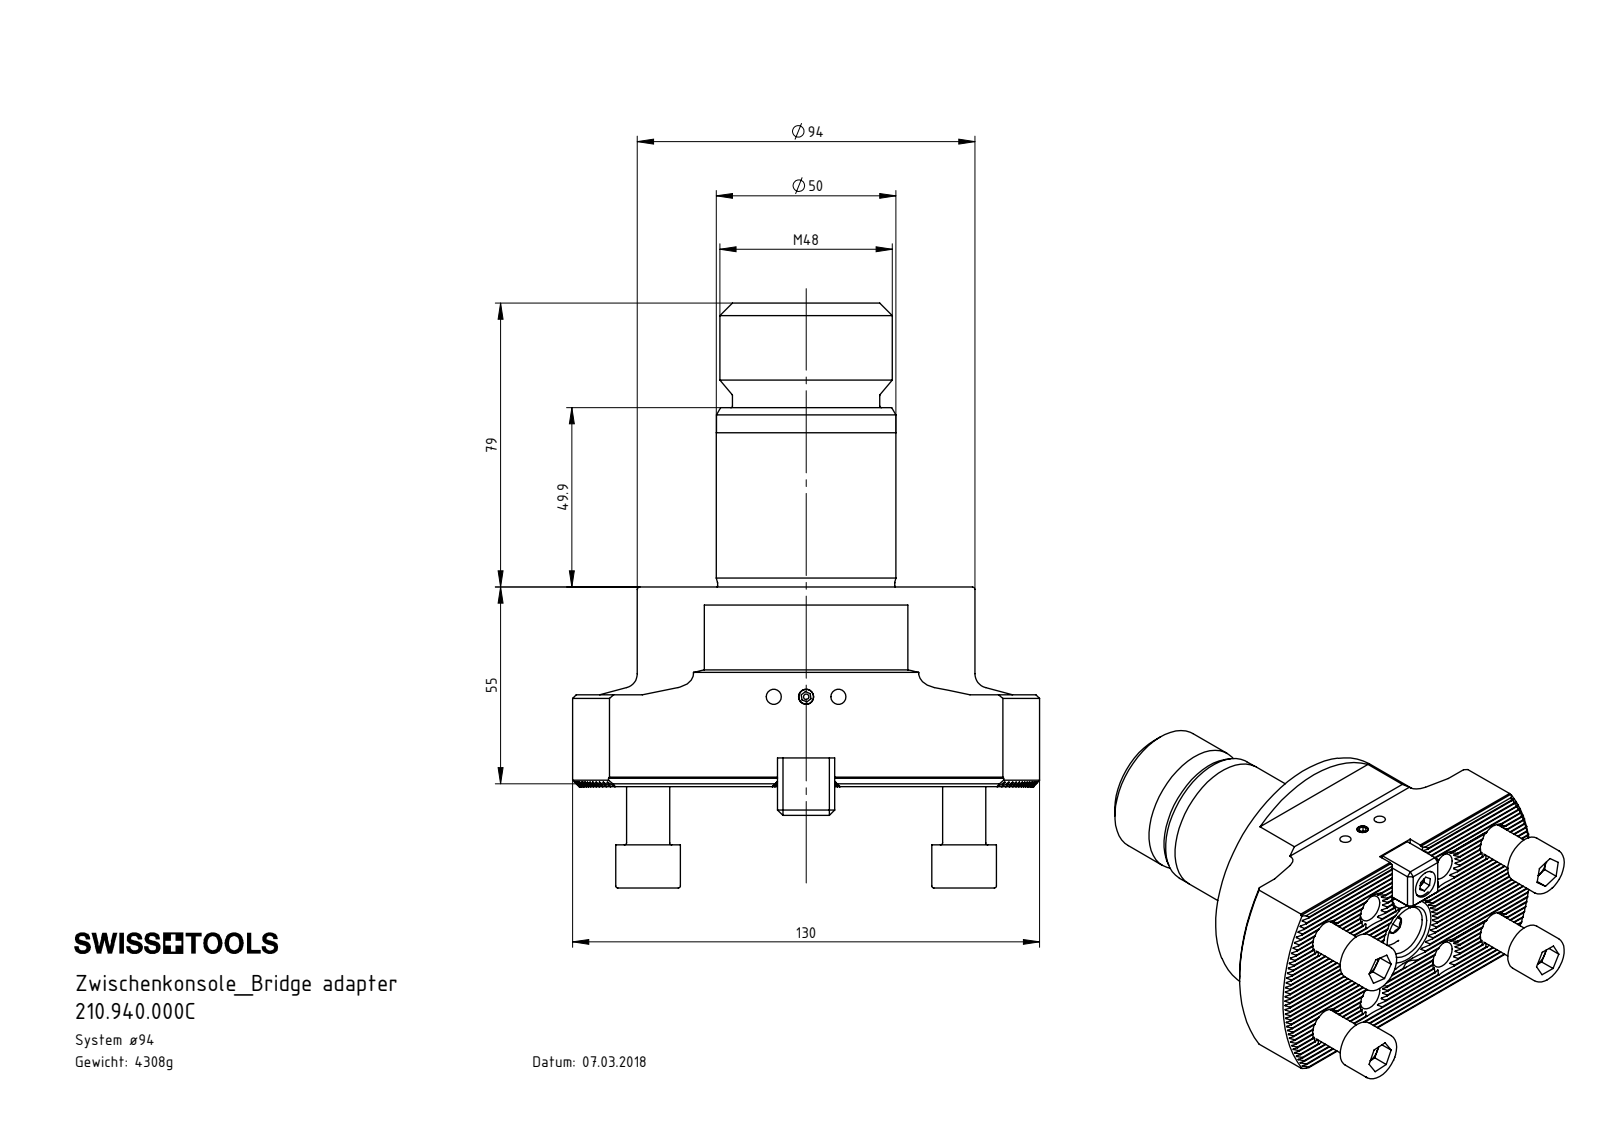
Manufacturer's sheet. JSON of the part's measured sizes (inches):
{"part_name": "210.940.000C; DIN 908 - M12x1.5; ISO 4026 - M5 x 8_ISO 4026 - M5 x 8; ISO 4762 M12 x 25 (+3 more)", "step_written_by": "SolidWorks 2017 (CONFIG_CONTROL_DESIGN)", "units": "inches", "bodies": {"solids": 10, "faces": 830, "planar": 480, "cylindrical": 195, "other": 155}, "overall_size": [6.408, 5.118, 3.701], "volume_in3": 33.49, "surface_area_in2": 120.6, "round_holes": [[0.402, 8], [0.165, 3], [0.413, 2], [0.059, 1], [0.197, 1], [0.256, 1], [0.285, 1], [0.335, 1], [0.748, 1]], "round_bosses_or_shafts": [[0.472, 5], [0.709, 4], [3.701, 1], [1.969, 1], [1.967, 1], [1.941, 1], [1.89, 1], [1.614, 1]], "partial_cylinders_radius": [[0.006, 34], [0.313, 1], [2.559, 1]], "face_to_face_distances": [0.068, 0.682, 2.756, 0.341, 0.136, 0.205, 0.273, 0.098, 0.614, 2.854], "hole_center_spacings": [0.984, 1.086, 1.575, 1.857, 1.903, 2.48, 2.938, 0.354]}
